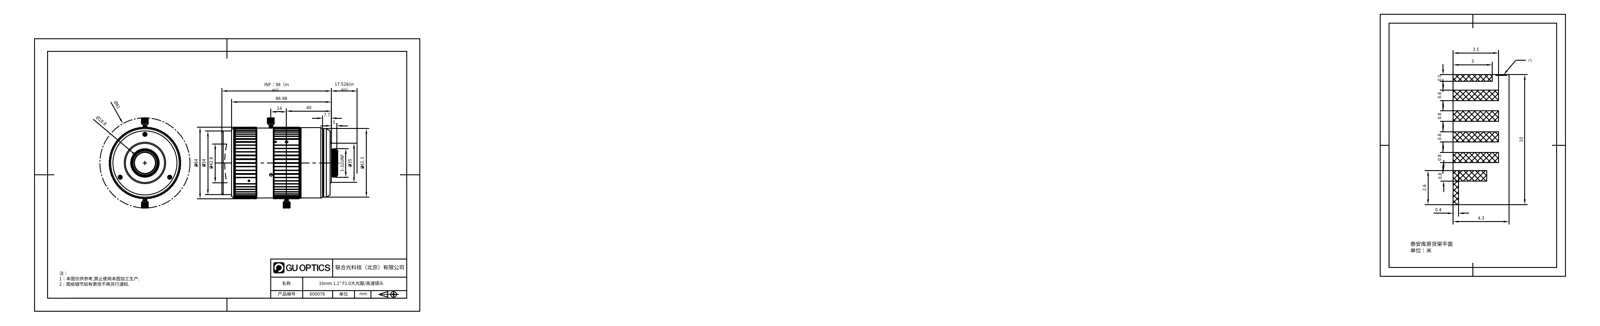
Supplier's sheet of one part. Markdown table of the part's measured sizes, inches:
| quantity | value |
| --- | --- |
| part name | 600076 |
| STEP written by | SolidWorks 2020 (CONFIG_CONTROL_DESIGN) |
| units | inches |
| bodies | 0 solids, 1356 faces (550 planar, 518 cylindrical, 288 other) |
| overall size | 4.09 × 3.173 × 2.52 |
| round holes (diameter × count) | 0.059 × 14, 0.063 × 11, 0.049 × 6, 0.098 × 6, 0.138 × 6, 0.083 × 3, 0.146 × 3, 0.126 × 2, 0.74 × 1, 0.748 × 1, 0.756 × 1, 0.795 × 1 |
| round bosses / shafts (diameter × count) | 0.079 × 14, 0.118 × 8, 0.063 × 6, 0.197 × 2, 0.087 × 2, 2.52 × 1, 2.492 × 1, 2.48 × 1 |
| partial cylindrical surfaces (radius × count) | 0.004 × 103, 0.069 × 6, 0.039 × 4, 0.079 × 4, 0.118 × 2, 0.876 × 1, 0.892 × 1, 0.967 × 1 |
| main face-to-face distances | 0.11, 0.059, 0.323, 1.969, 2.181, 2.291, 0.362, 1.178, 1.85, 0.205 |
| hole center spacings | 0.807, 1.008, 0.386, 1.07, 1.602, 1.328, 1.509, 0.75 |
